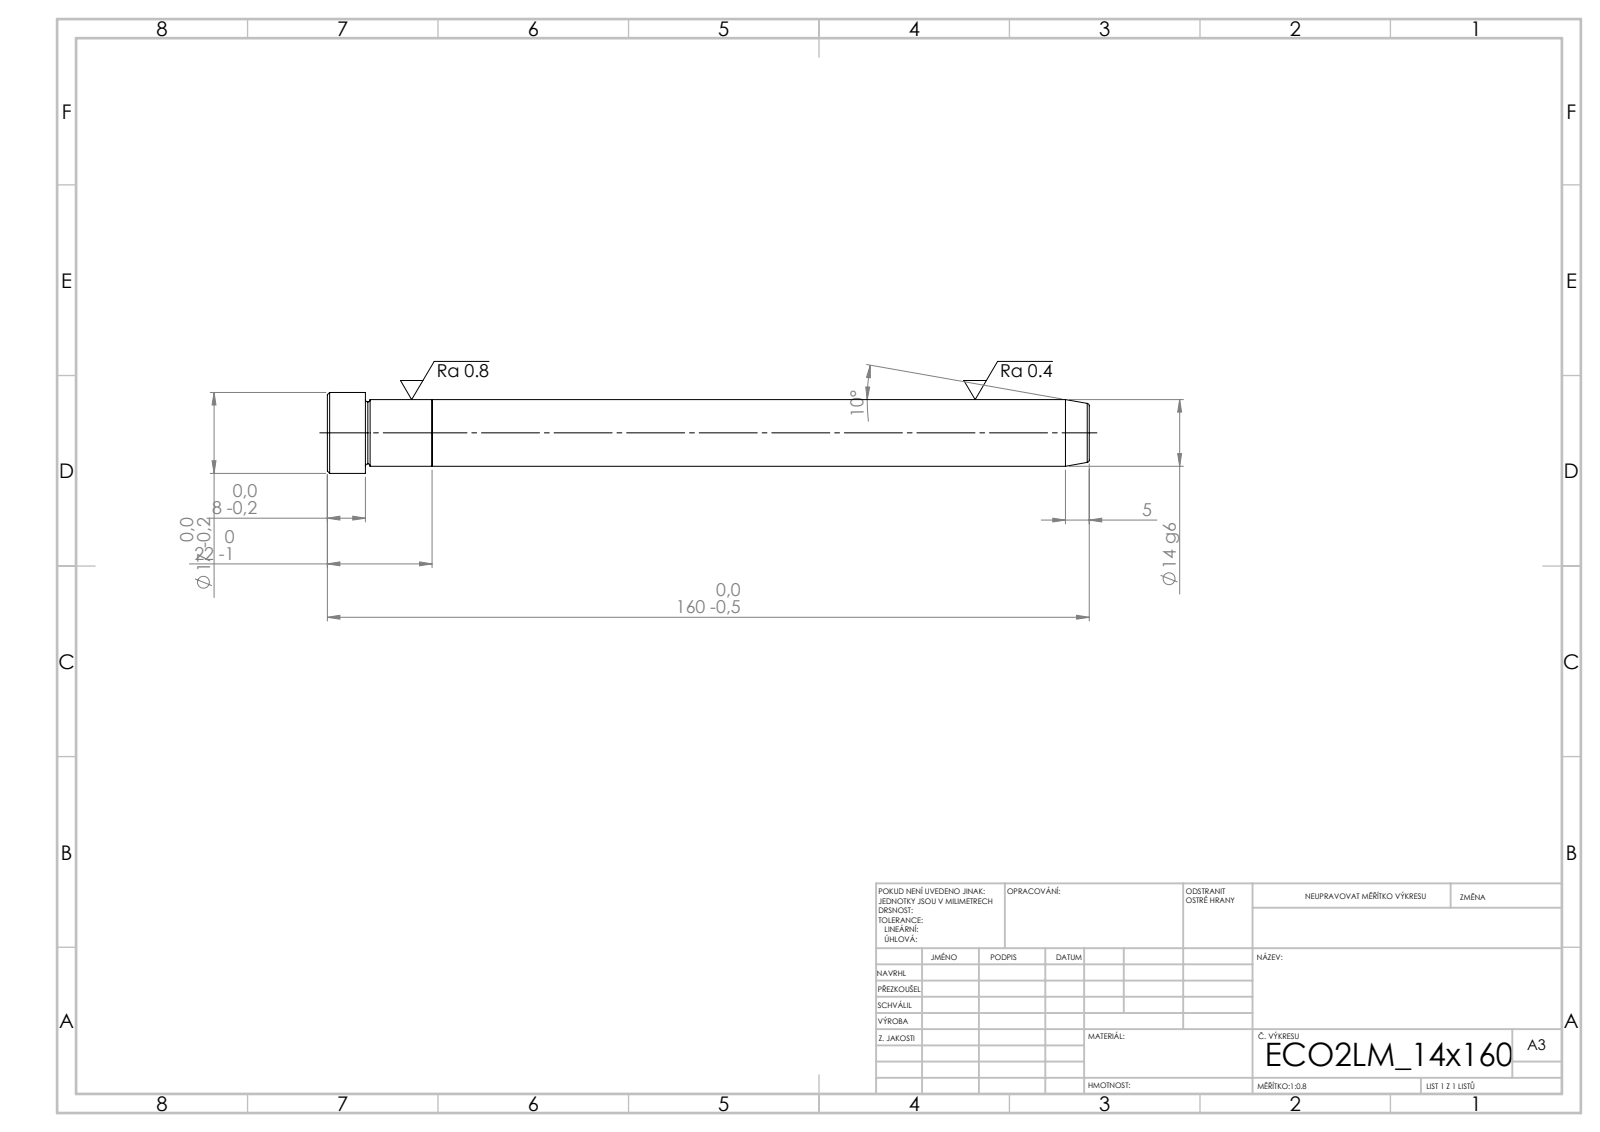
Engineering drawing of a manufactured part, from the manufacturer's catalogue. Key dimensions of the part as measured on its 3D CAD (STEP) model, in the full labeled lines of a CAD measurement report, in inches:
STEP written by: SolidWorks 2019 (CONFIG_CONTROL_DESIGN)
Units: inches
Bodies: 2 solids, 21 faces (5 planar, 6 cylindrical, 10 other)
Overall size (bounding box): 6.299 × 0.669 × 0.669
Volume: 1.532 in³ · Surface area: 12.13 in²
Round bosses / shafts (diameter × count): ⌀0.669 ×1, ⌀0.551 ×1
Main face-to-face distances: 0.866, 5.433, 6.299, 5.984, 0.551, 0.315
